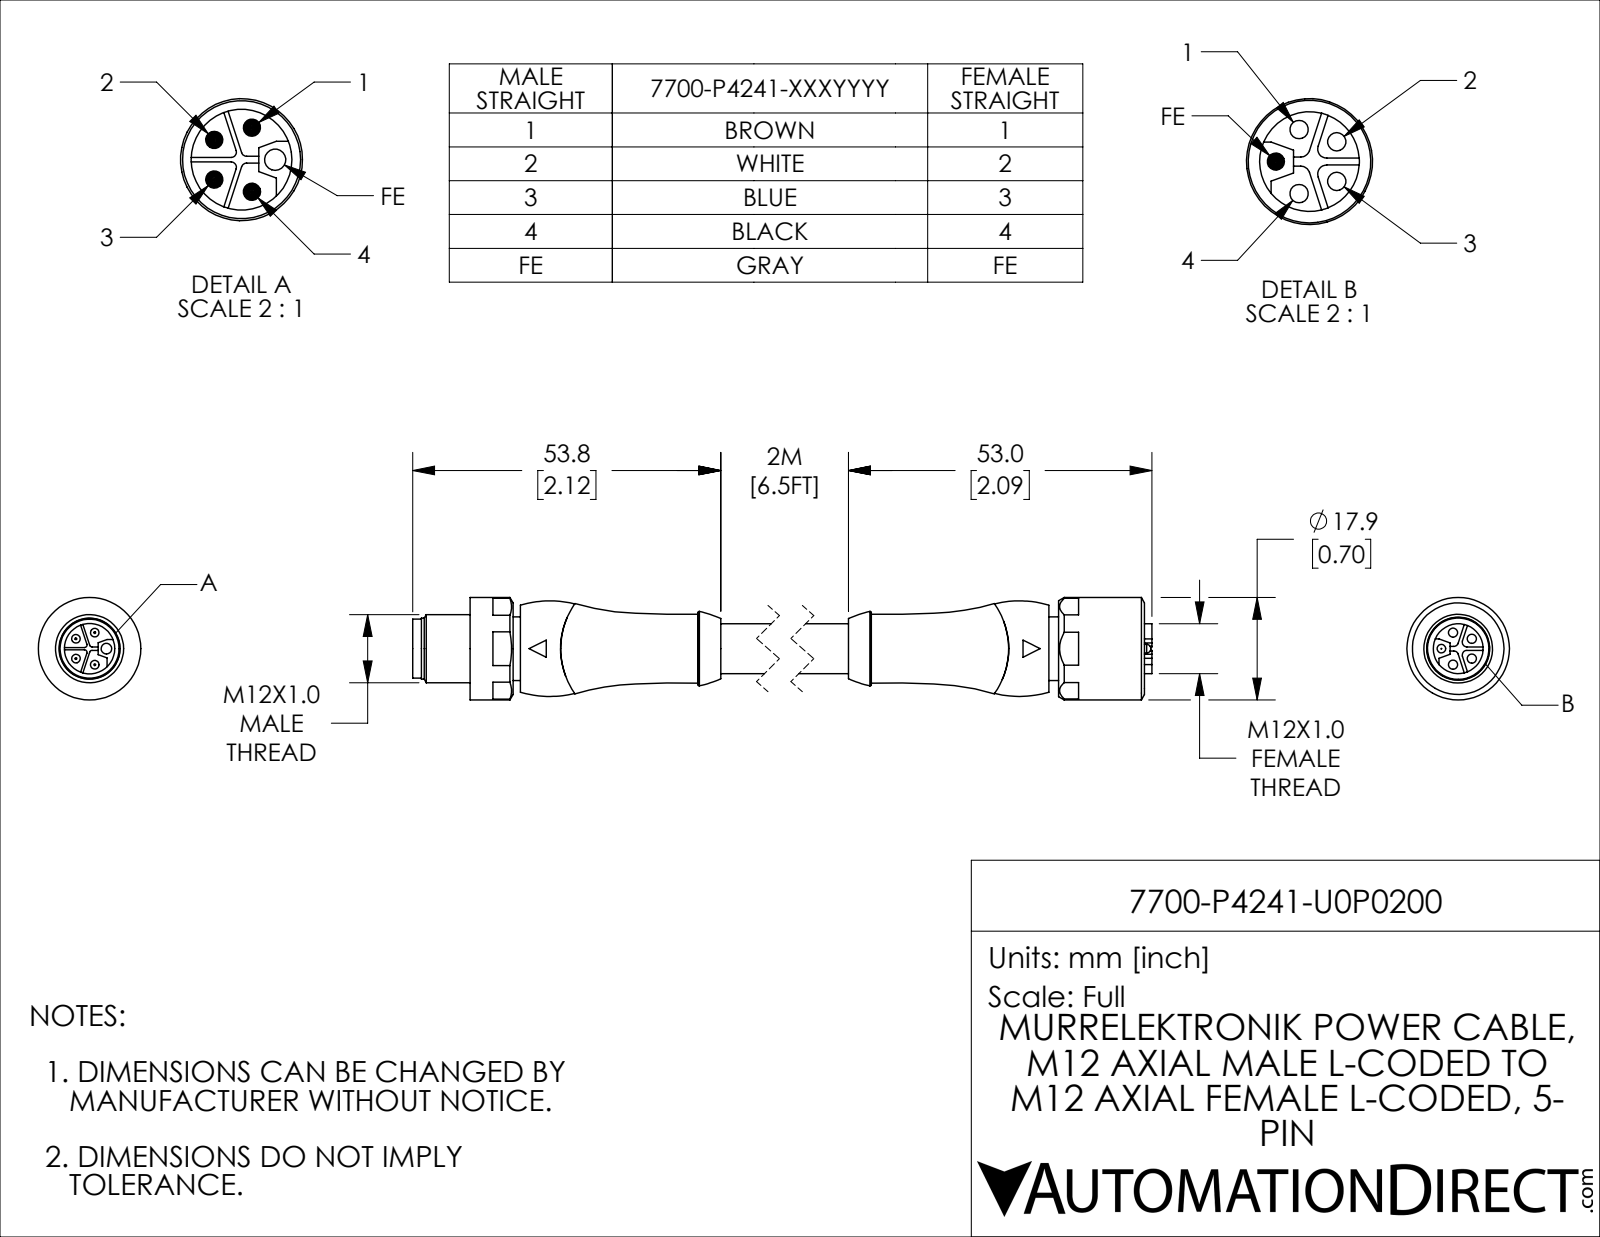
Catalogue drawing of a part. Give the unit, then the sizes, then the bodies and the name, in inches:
Units: inches
Overall size (bounding box): 5.386 × 0.705 × 0.705
Round holes (diameter × count): ⌀0.063 ×4, ⌀0.073 ×1, ⌀0.346 ×1, ⌀0.433 ×1, ⌀0.512 ×1
Round bosses / shafts (diameter × count): ⌀0.059 ×5, ⌀0.705 ×1, ⌀0.51 ×1, ⌀0.469 ×1, ⌀0.437 ×1, ⌀0.419 ×1, ⌀0.406 ×1, ⌀0.343 ×1
Partial cylindrical surfaces — rounded edges, fillets, slot ends (radius × count): R0.018 ×4, R0.031 ×4
Main face-to-face distances: 4.283, 0.067, 0.346, 0.666, 0.051, 0.295, 0.228, 4.941, 0.657, 4.35
Hole centre spacings: 0.116, 0.136, 0.22, 0.22
Volume: 1.09 in³ · Surface area: 14.44 in²
Bodies: 3 solids, 214 faces (98 planar, 62 cylindrical, 54 other)
Part name (STEP PRODUCT): 7700-P4241-U0P0200; 7700-P4241-U0P0200_1; 7700-P4241-U0P0200_2
STEP written by: SolidWorks 2021 (CONFIG_CONTROL_DESIGN)
